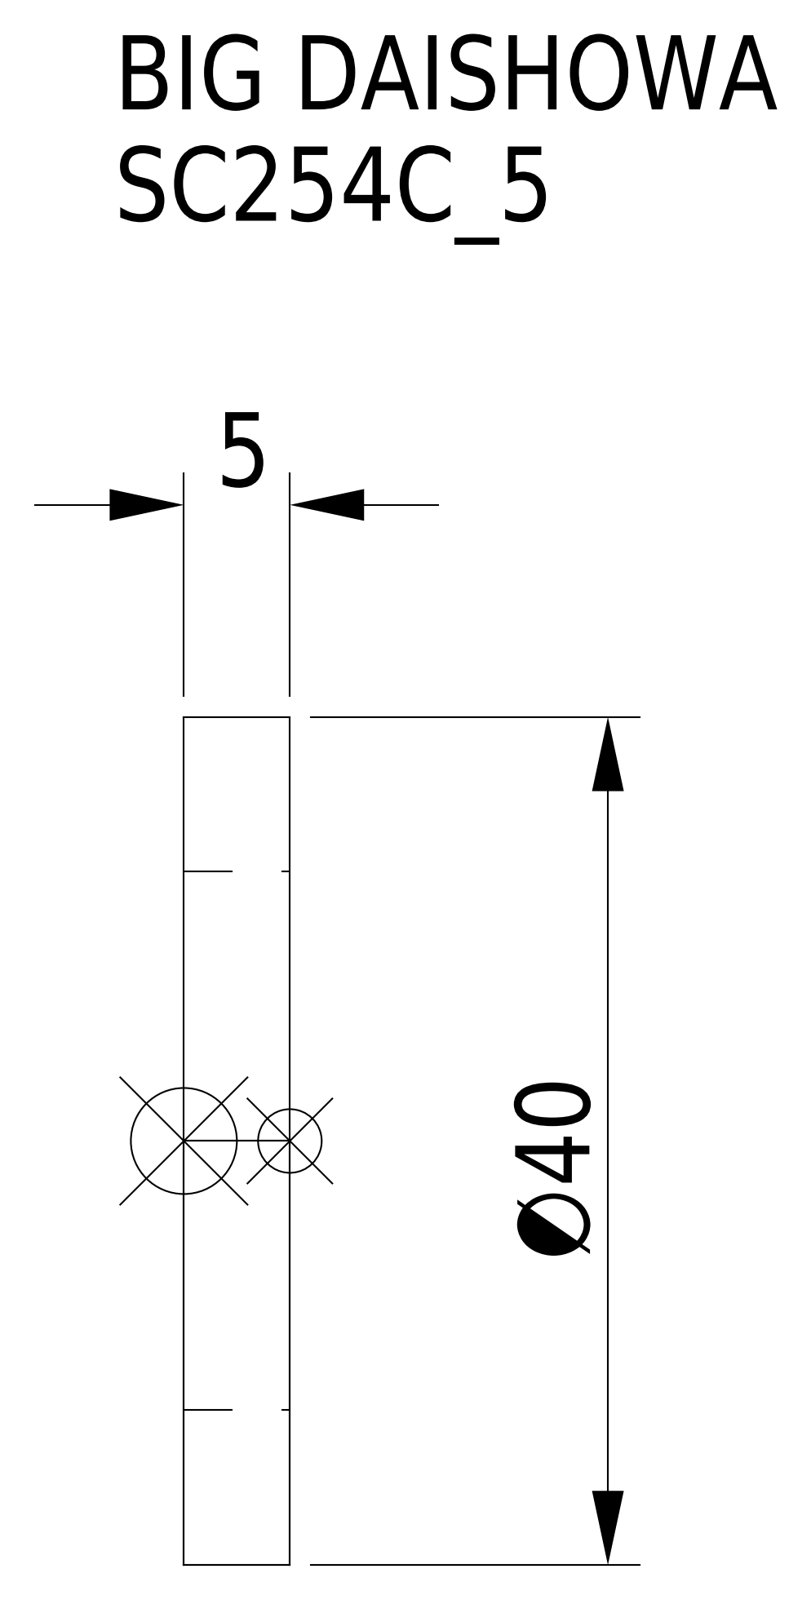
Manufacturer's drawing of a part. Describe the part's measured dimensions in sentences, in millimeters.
The part is named "SC254C_5". Its 3-D file was written by "CREO PARAMETRIC BY PTC INC, 2016380 (AUTOMOTIVE_DESIGN)". It is 1 solid with 8 faces: 5 planar, 3 cylindrical and 0 other. Overall it measures 40 by 40 by 5 millimeters. Its volume is 3 657 cubic millimeters and its surface area 2 521 square millimeters. Round holes: 1 of diameter 25.4. Round bosses or shafts: 1 of diameter 40. The main face-to-face distances are 5, 6.5.
